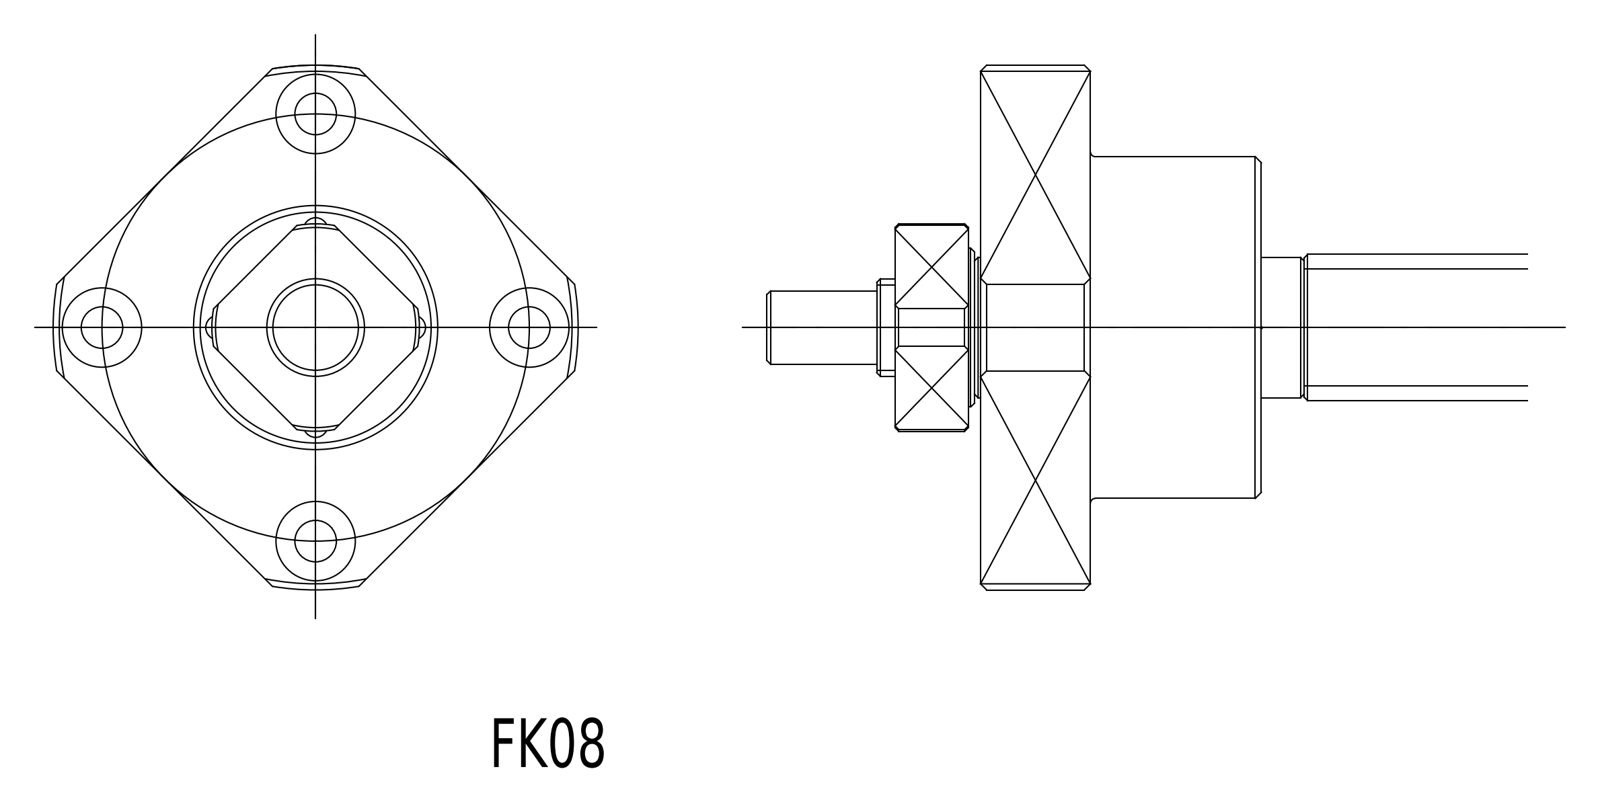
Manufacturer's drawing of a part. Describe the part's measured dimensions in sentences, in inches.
Its 3-D file was written by "SolidWorks 2008 (CONFIG_CONTROL_DESIGN)". It is 30 solids with 1449 faces: 200 planar, 454 cylindrical and 795 other. Overall it measures 1.378 by 1.378 by 1.24 inches. Its volume is 0.991 cubic inches and its surface area 26.29 square inches. Round holes: 4 of diameter 0.134, 4 of diameter 0.256, 3 of diameter 0.098, 2 of diameter 0.102, 1 of diameter 0.276, 1 of diameter 0.315, 1 of diameter 0.432, 1 of diameter 0.472, 1 of diameter 0.516, 1 of diameter 0.591, 1 of diameter 0.634, 1 of diameter 0.715. Round bosses or shafts: 1 of diameter 1.102, 1 of diameter 0.945, 1 of diameter 0.866, 1 of diameter 0.642, 1 of diameter 0.63, 1 of diameter 0.512, 1 of diameter 0.478, 1 of diameter 0.453. Partial cylindrical surfaces (rounded edges, fillets, slot ends): 196 of radius 0.004, 14 of radius 0.075, 1 of radius 0.846. The main face-to-face distances are 0.276, 0.551, 0.157, 0.272, 0.197, 0.024, 0.252, 0.02, 0.248, 0.748. The hole center spacings are 0.689, 0.974, 0.354, 0.359, 0.505, 0.614, 0.688, 0.852.
